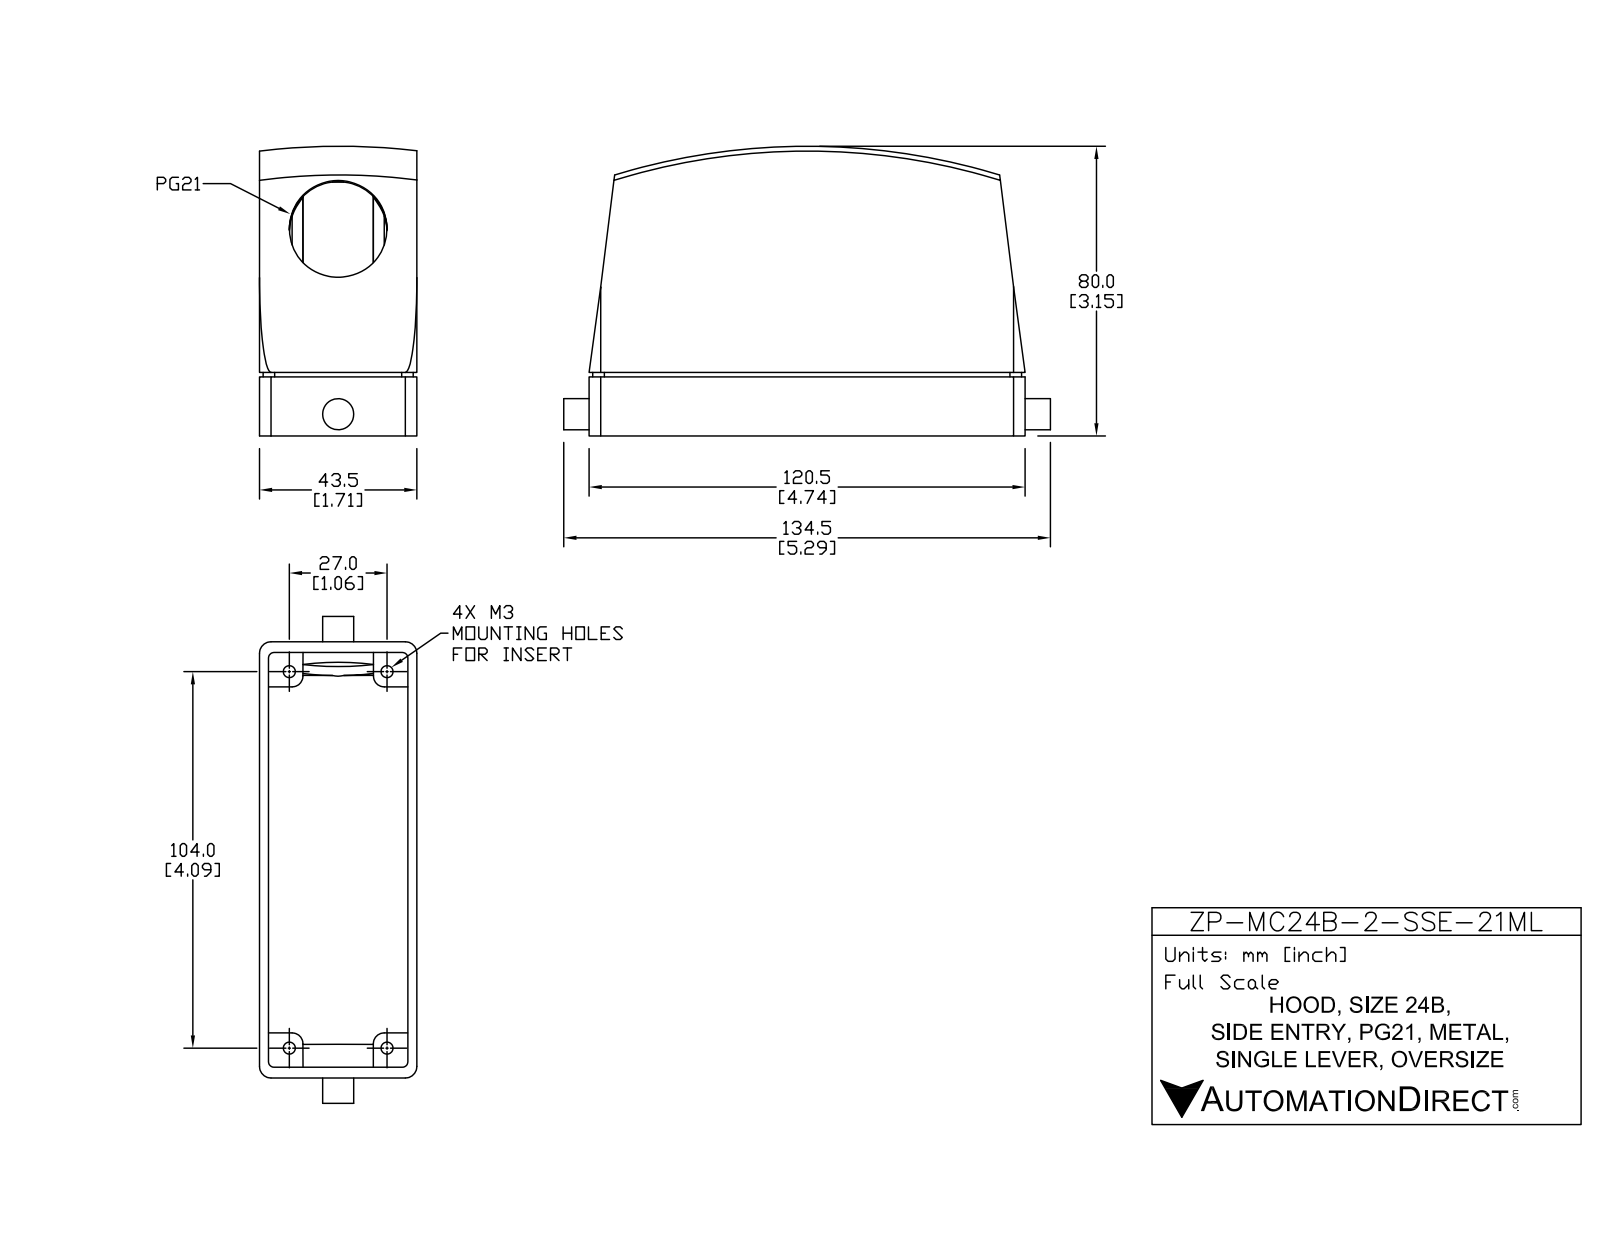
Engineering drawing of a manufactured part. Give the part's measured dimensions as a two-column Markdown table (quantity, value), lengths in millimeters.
| quantity | value |
| --- | --- |
| part name | ZP-MC24B-2-SSE21ML |
| STEP written by | SolidWorks 2011 (AUTOMOTIVE_DESIGN) |
| units | millimeters |
| bodies | 5 solids, 92 faces (54 planar, 32 cylindrical, 6 other) |
| overall size | 134.5 × 77.55 × 43.5 |
| volume | 79 509 mm³ |
| surface area | 61 437 mm² |
| round holes (diameter × count) | 3.3 × 4, 27 × 1 |
| round bosses / shafts (diameter × count) | 8.6 × 1 |
| partial cylindrical surfaces (radius × count) | 3.2 × 8, 1.5 × 4, 3 × 4, 0.7 × 1 |
| main face-to-face distances | 2.5, 41, 43.5, 38.5, 9.5, 105.08, 2.96, 12.46, 108.04, 117.54 |
| hole center spacings | 27, 104, 107.45 |
